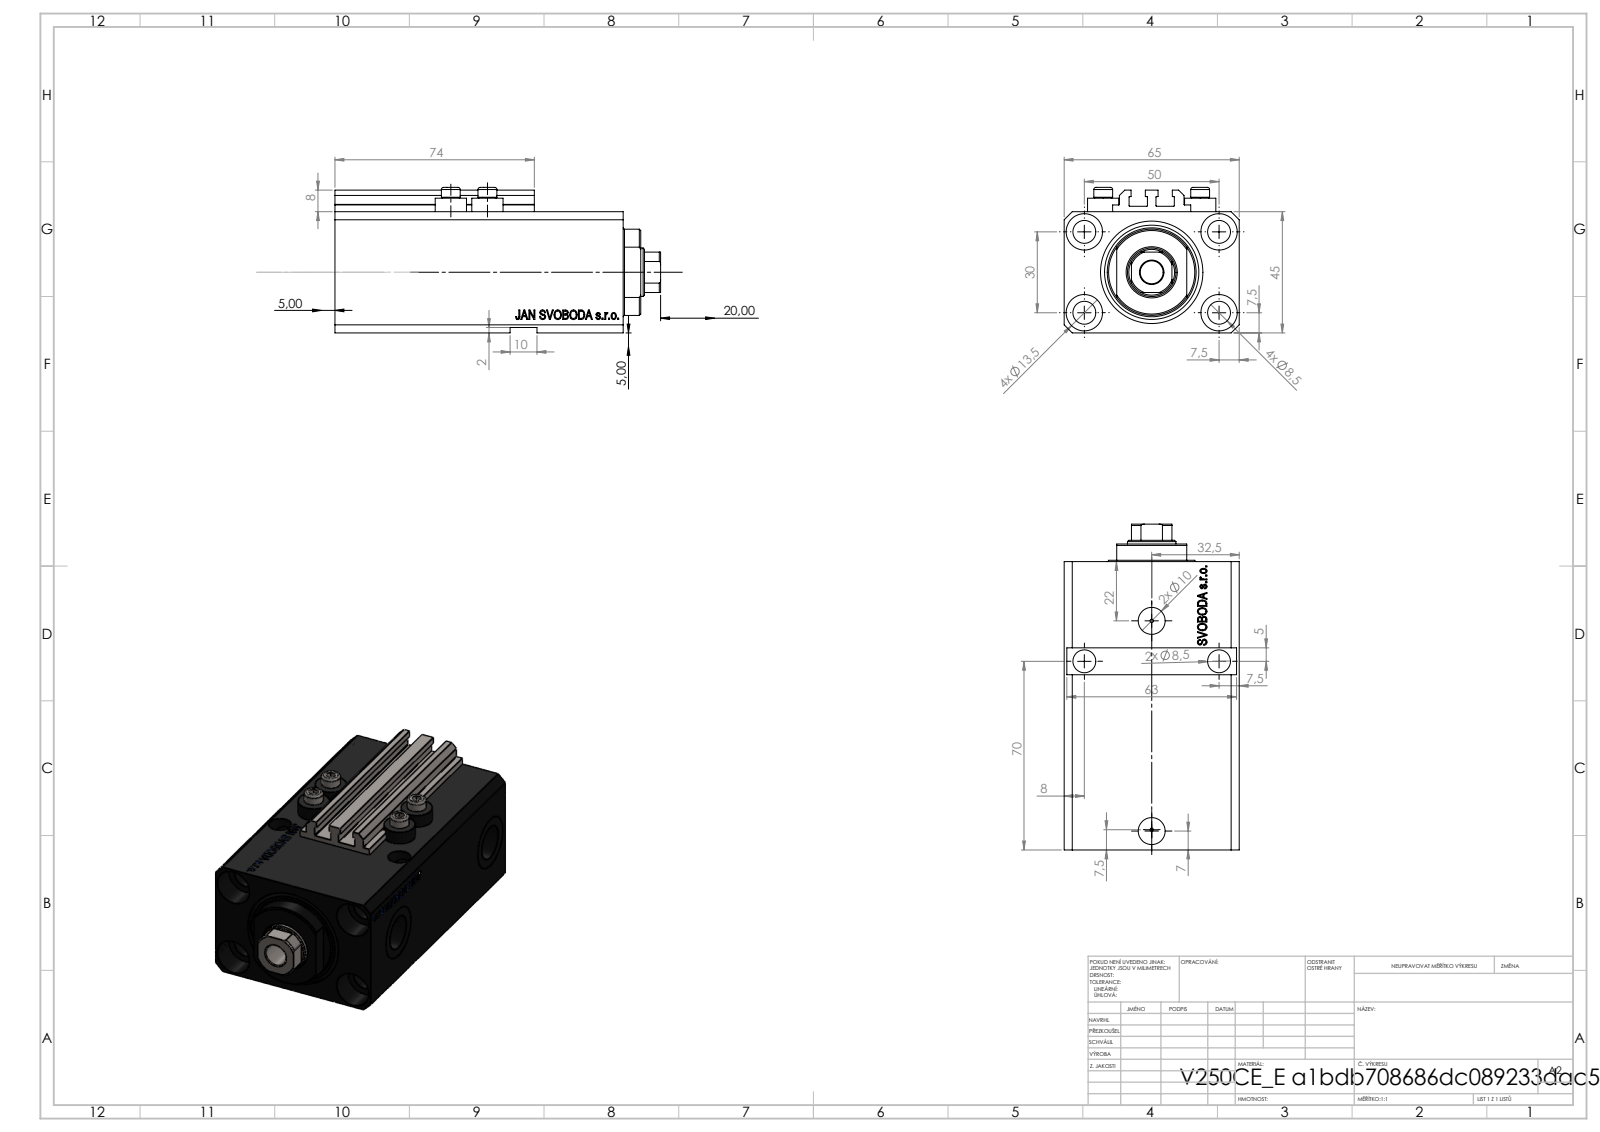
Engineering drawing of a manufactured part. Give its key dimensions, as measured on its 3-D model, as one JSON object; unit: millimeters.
{"part_name": "V250CE_C_VCP; ALLEN BOLT V250CE; V250CE_E_Body; V250CE_VC_E", "step_written_by": "SolidWorks 2019 (CONFIG_CONTROL_DESIGN)", "units": "millimeters", "bodies": {"solids": 8, "faces": 1087, "planar": 511, "cylindrical": 146, "other": 430}, "overall_size": [121, 65, 54], "volume_mm3": 273399, "surface_area_mm2": 76876, "round_holes": [[8.5, 9], [1.25, 4], [4, 4], [13.5, 4], [10, 2], [13.16, 2], [20, 2], [18, 1], [25, 1], [38, 1]], "round_bosses_or_shafts": [[11.6, 4], [7, 4]], "partial_cylinders_radius": [[0.2, 10], [8.5, 1], [16, 1]], "face_to_face_distances": [45, 65, 93, 2, 14, 47, 107, 2.5, 10, 20.5], "hole_center_spacings": [29.15, 50, 13.6, 14.76, 15.12, 27.51, 27.89, 30]}
